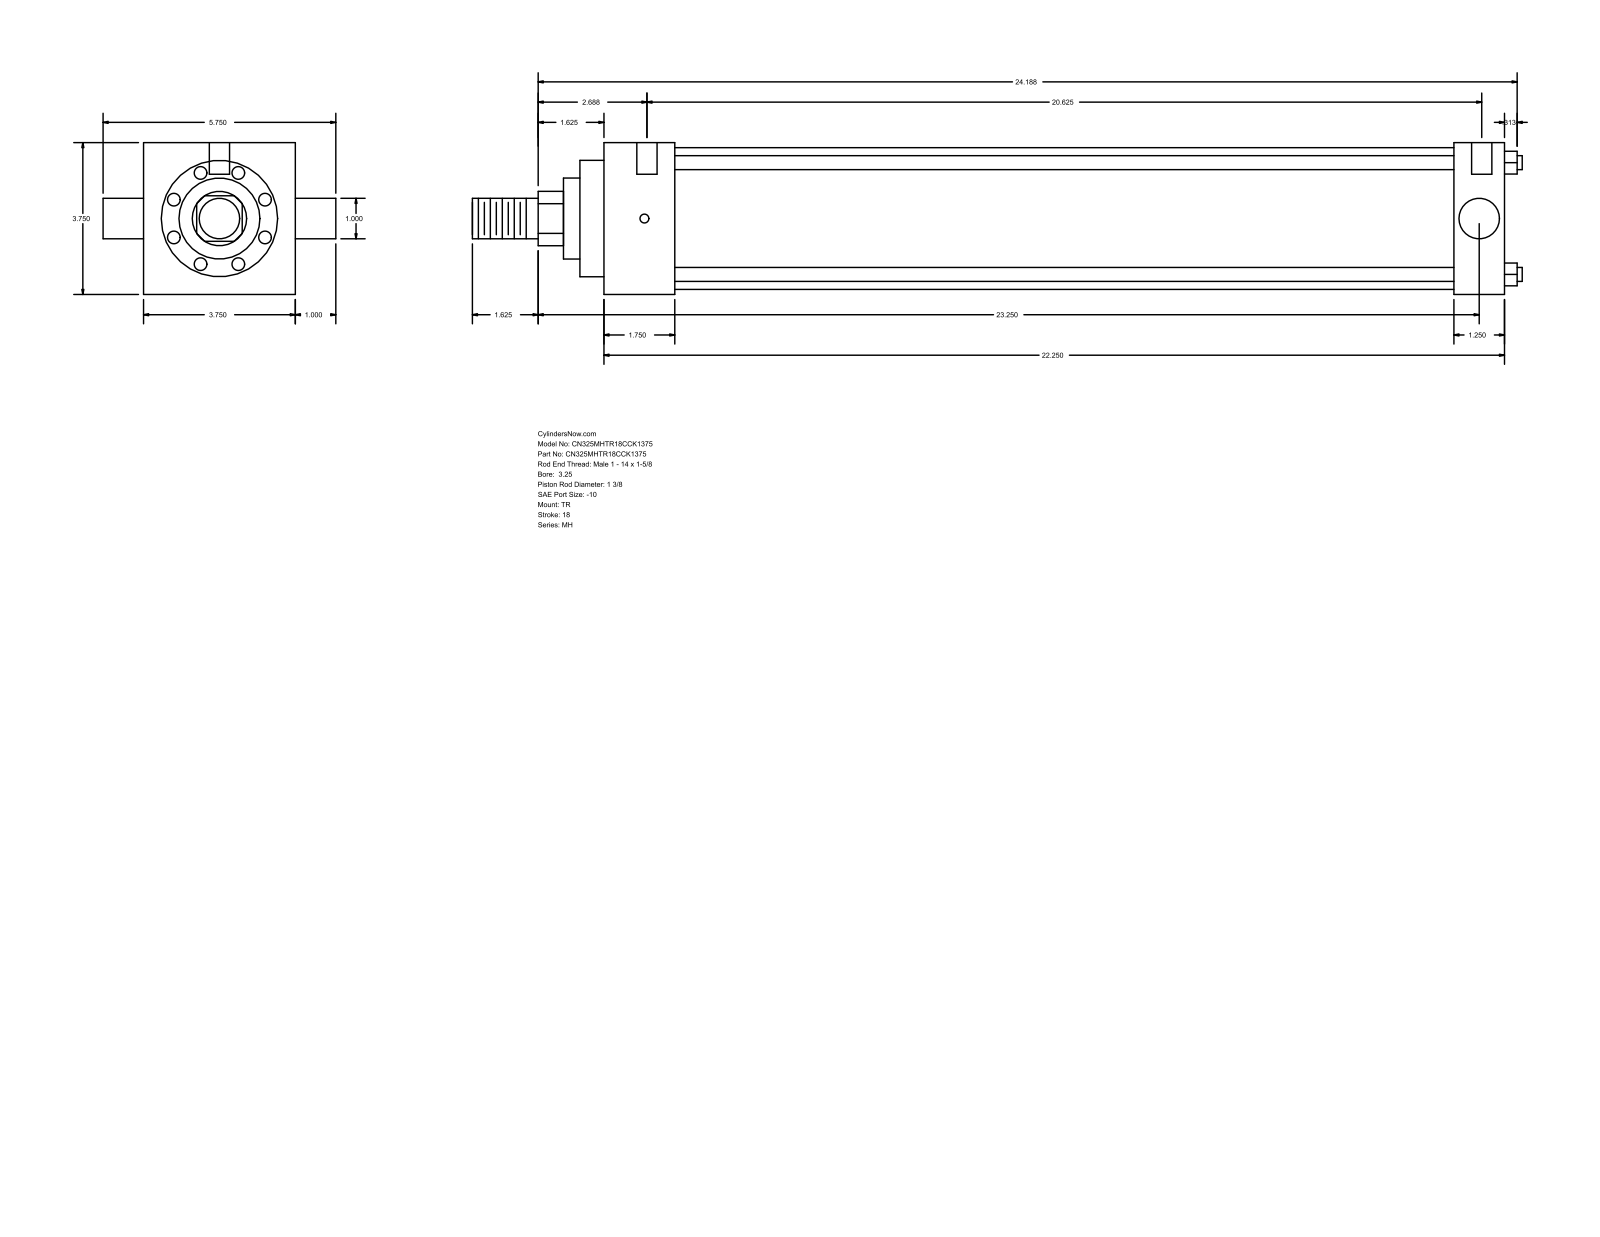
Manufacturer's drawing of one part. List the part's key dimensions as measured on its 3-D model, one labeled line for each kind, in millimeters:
Part name (STEP PRODUCT): MH_TR__0325_1.375
STEP written by: GSSL Pune (CONFIG_CONTROL_DESIGN)
Units: millimetres
Bodies: 0 solids, 86 faces (61 planar, 25 cylindrical, 0 other)
Overall size (bounding box): 658.81 × 146.05 × 95.25
Round holes (diameter × count): ⌀5.56 ×3, ⌀12.7 ×2
Round bosses / shafts (diameter × count): ⌀8.76 ×4, ⌀25.4 ×2, ⌀88.9 ×1, ⌀73.03 ×1, ⌀50.8 ×1, ⌀34.92 ×1
Partial cylindrical surfaces — rounded edges, fillets, slot ends (radius × count): R17.06 ×1
Main face-to-face distances: 95.24, 565.15, 44.45, 533.4, 488.95, 520.7, 31.75, 15.08, 59.53, 548.48
Hole centre spacings: 1.59, 4.76, 523.88, 525.47, 528.64, 530.23
